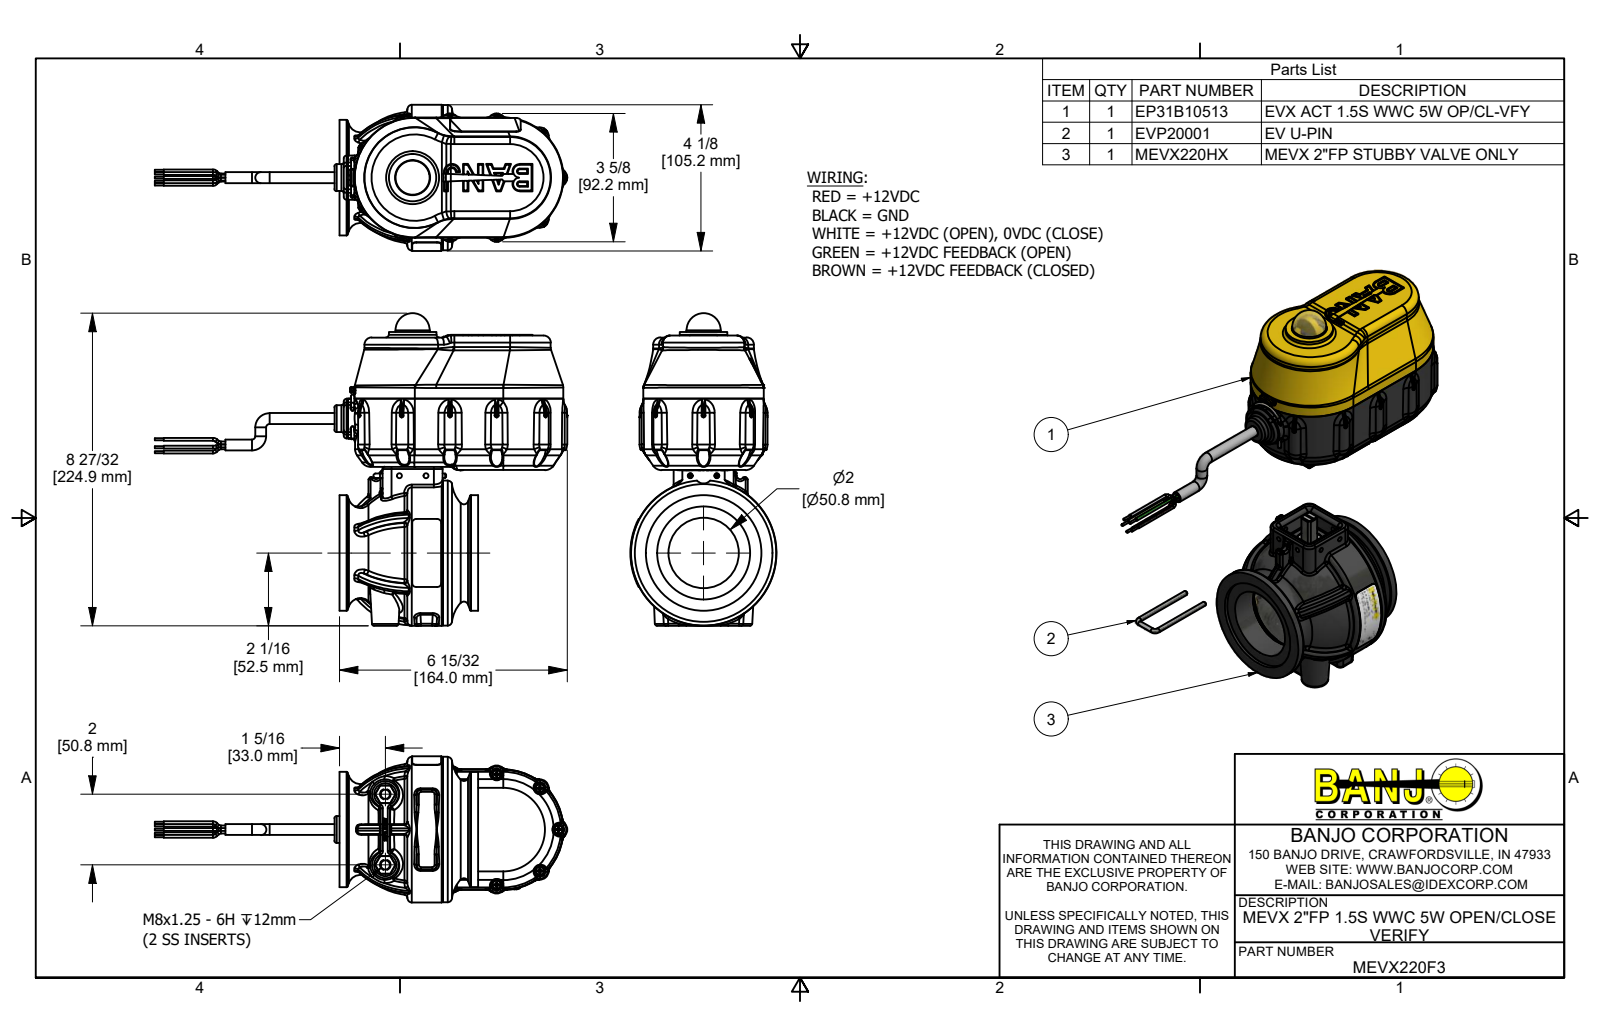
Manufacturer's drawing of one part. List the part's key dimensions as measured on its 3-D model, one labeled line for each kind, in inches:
Part name (STEP PRODUCT): MEVX220F3; EP31B10513; B61905PPHS; B632038PM (+8 more)
STEP written by: Autodesk Inventor 2019 (AUTOMOTIVE_DESIGN)
Units: inches
Bodies: 84 solids, 10831 faces (2811 planar, 3111 cylindrical, 4909 other)
Overall size (bounding box): 11.685 × 8.856 × 4.14
Volume: 53.17 in³ · Surface area: 608.8 in²
Round holes (diameter × count): ⌀0.095 ×11, ⌀0.15 ×11, ⌀0.08 ×7, ⌀0.135 ×5, ⌀0.107 ×4, ⌀0.126 ×4, ⌀0.136 ×4, ⌀0.148 ×4, ⌀0.15 ×4, ⌀0.17 ×4, ⌀0.105 ×2, ⌀0.118 ×2
Round bosses / shafts (diameter × count): ⌀0.08 ×25, ⌀0.25 ×17, ⌀0.14 ×11, ⌀0.108 ×11, ⌀0.085 ×11, ⌀0.058 ×10, ⌀0.27 ×4, ⌀0.219 ×4
Partial cylindrical surfaces — rounded edges, fillets, slot ends (radius × count): R0.013 ×180, R0.04 ×145, R0.01 ×92, R0.02 ×71, R0.005 ×55, R0.03 ×34, R0.06 ×31, R0.08 ×28
Main face-to-face distances: 0.1, 2.565, 0.06, 0.211, 0.151, 1.896, 1.836, 1.685, 0.569, 0.629
Hole centre spacings: 2.22, 1.283, 2.69, 2.715, 1.662, 1.774, 2.73, 3.789
